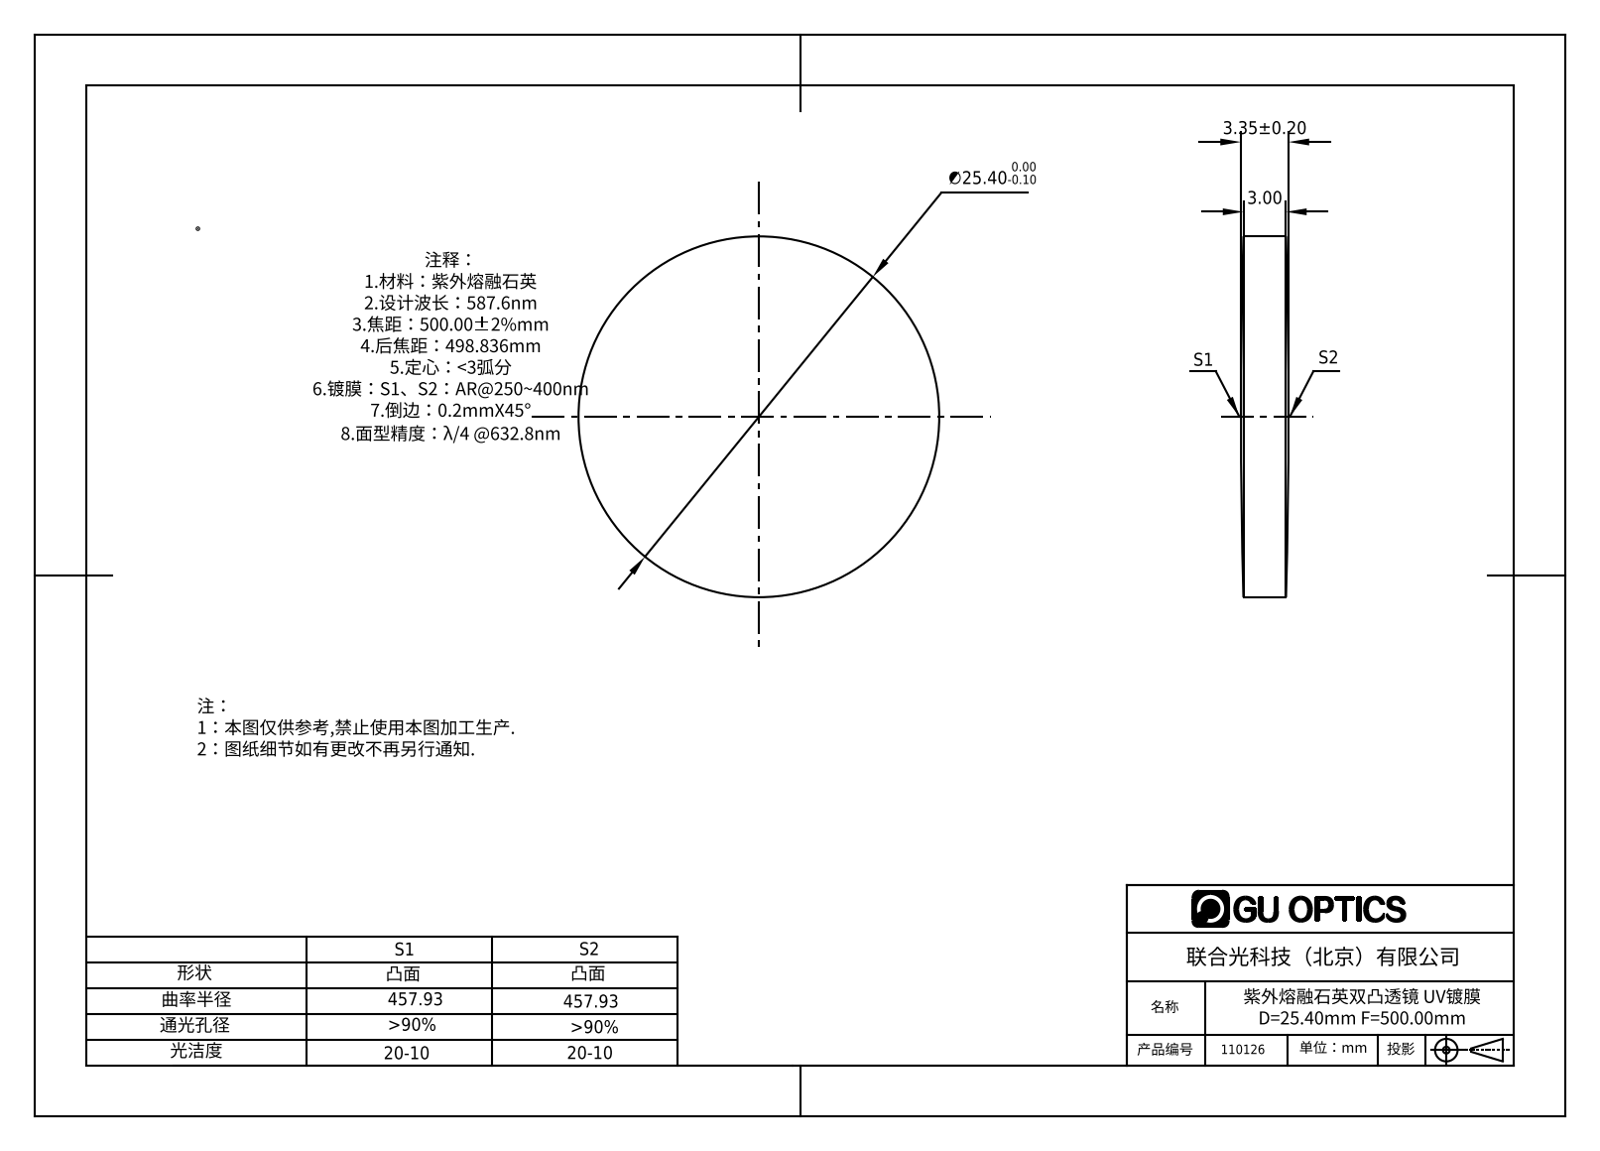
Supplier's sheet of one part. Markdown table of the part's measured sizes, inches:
| quantity | value |
| --- | --- |
| part name | 11012 |
| STEP written by | SolidWorks 2016 (CONFIG_CONTROL_DESIGN) |
| units | inches |
| bodies | 1 solid, 6 faces (0 planar, 2 cylindrical, 4 other) |
| overall size | 1 × 1 × 0.132 |
| volume | 0.098 in³ |
| surface area | 1.942 in² |
| round bosses / shafts (diameter × count) | 1 × 1 |
